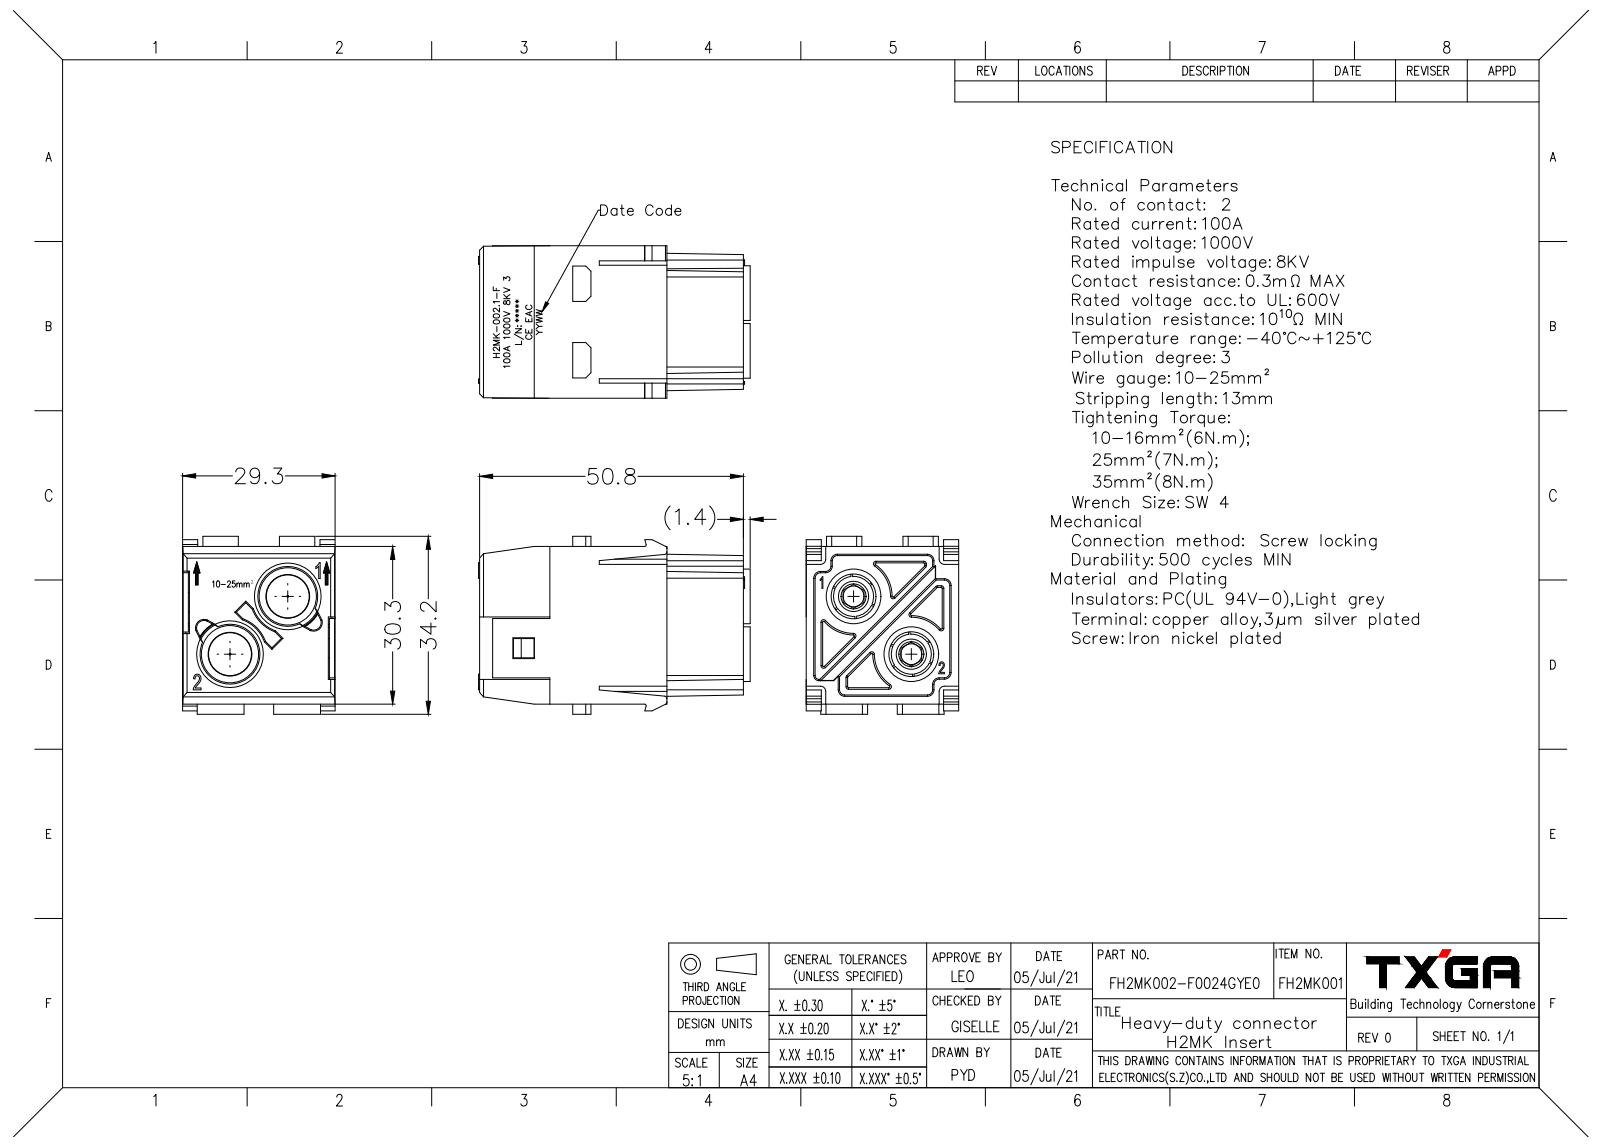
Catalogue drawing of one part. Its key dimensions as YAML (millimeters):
part_name: "FH2MK002-F0024GYE0 H2MK-002.1-F"
step_written_by: "SolidWorks 2021 (CONFIG_CONTROL_DESIGN)"
units: millimeters
bodies: {solids: 1, faces: 873, planar: 384, cylindrical: 205, other: 284}
overall_size: [52.2, 34.2, 29.3]
volume: 25703
surface_area: 29511
round_holes:
  - {diameter: 4, count: 2}
  - {diameter: 4.8, count: 2}
  - {diameter: 8, count: 2}
  - {diameter: 8.4, count: 2}
  - {diameter: 8.6, count: 2}
  - {diameter: 11.7, count: 2}
  - {diameter: 12, count: 2}
  - {diameter: 13.3, count: 2}
round_bosses_or_shafts:
  - {diameter: 2.3, count: 3}
  - {diameter: 13, count: 2}
  - {diameter: 10.5, count: 2}
  - {diameter: 8.25, count: 2}
  - {diameter: 7.55, count: 2}
  - {diameter: 7.2, count: 2}
  - {diameter: 6.65, count: 2}
  - {diameter: 6.05, count: 2}
partial_cylinders:
  - {radius: 0.19, count: 15}
  - {radius: 0.5, count: 15}
  - {radius: 0.31, count: 9}
  - {radius: 1, count: 6}
  - {radius: 1.35, count: 3}
  - {radius: 1.55, count: 3}
  - {radius: 0.3, count: 2}
  - {radius: 2, count: 2}
face_to_face_distances: [29.3, 1.3, 28, 1.1, 28.2, 30.3, 1, 26.9, 3.16, 1.86]
hole_center_spacings: [15.7]
